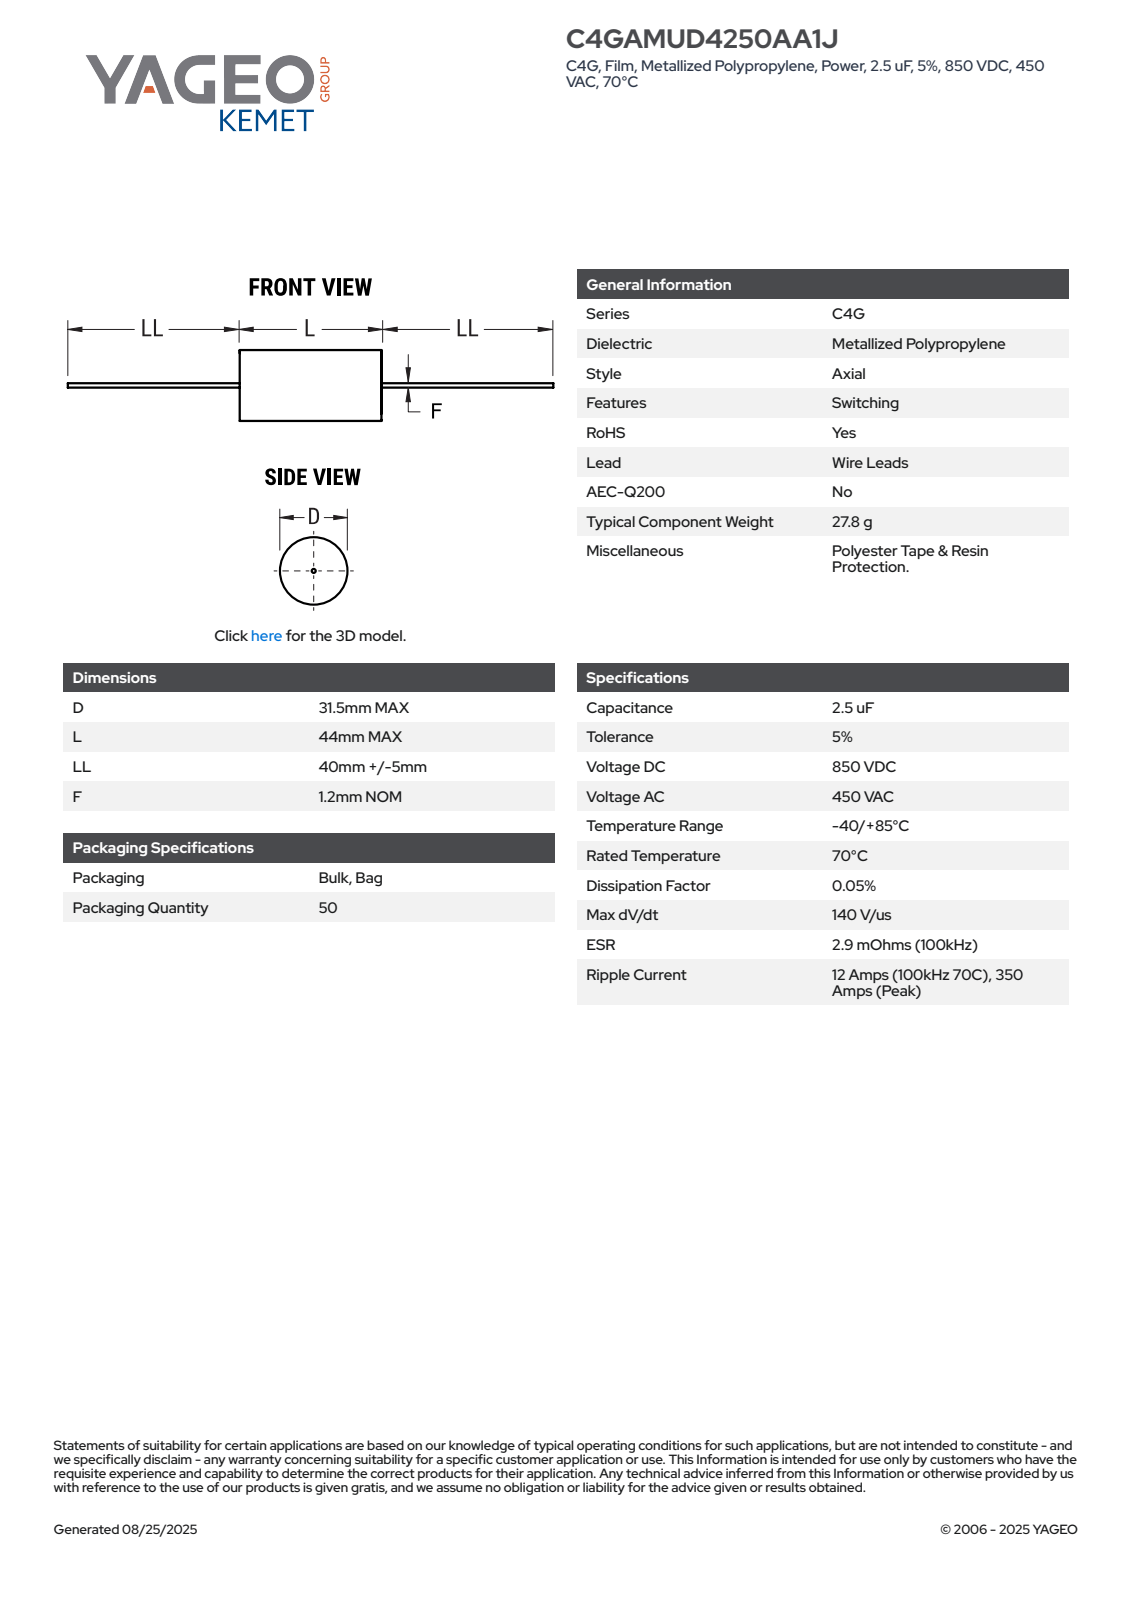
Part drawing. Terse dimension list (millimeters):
name: CFP_ACWF_31.5X44_D31.5L44LL45F1.2
written by: SolidWorks 2014 (AUTOMOTIVE_DESIGN)
unit: mm
bodies: 2 solids, 87 faces (28 planar, 28 cylindrical, 31 other)
size: 134 × 31.5 × 31.5
volume: 34 391 mm³; area: 7 809 mm²
bosses: 1× ⌀31.5, 1× ⌀1.2
rounds: 1× R15.74
face distances: 44, 43.99, 44.99, 45, 88.99, 134, 89.01, 89, 45.01
